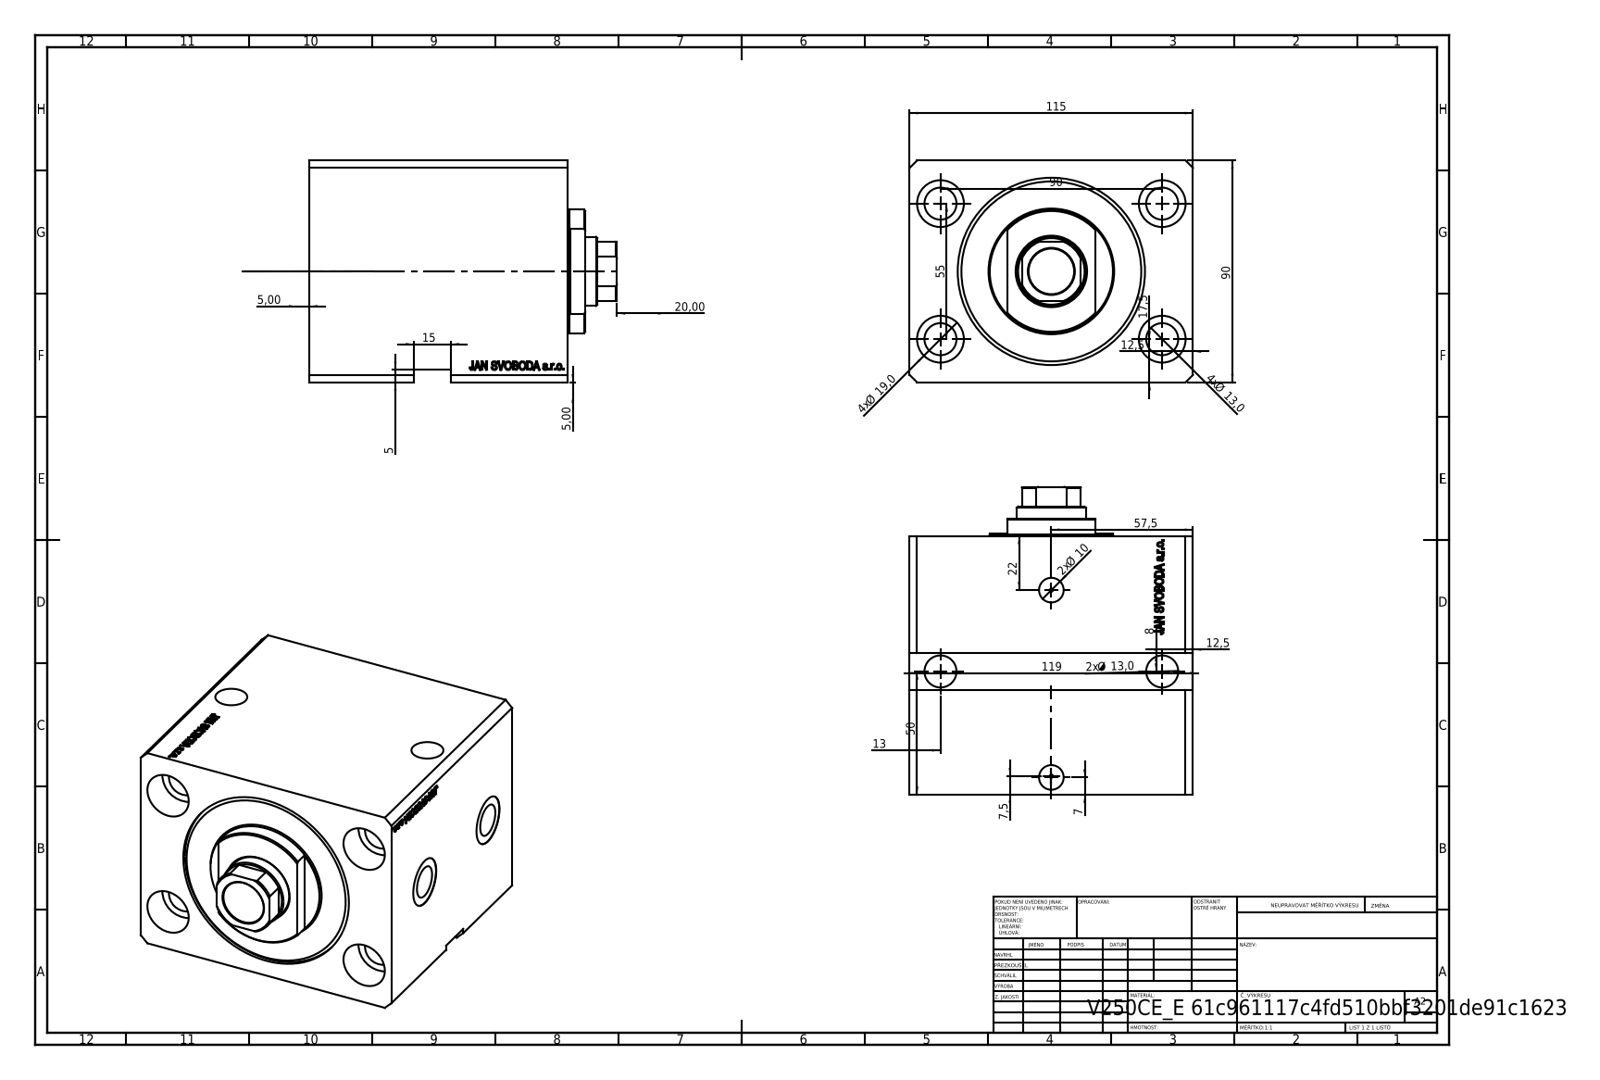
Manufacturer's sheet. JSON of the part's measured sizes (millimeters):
{"part_name": "V250CE_VC_E; V250CE_C_VCP; V250CE_E_Body", "step_written_by": "SolidWorks 2019 (CONFIG_CONTROL_DESIGN)", "units": "millimeters", "bodies": {"solids": 3, "faces": 937, "planar": 467, "cylindrical": 84, "other": 386}, "overall_size": [124.9, 115, 90], "volume_mm3": 942929, "surface_area_mm2": 146742, "round_holes": [[13, 6], [1.25, 4], [19, 4], [10, 2], [13.16, 2], [20, 2], [18.5, 1], [28, 1], [63, 1], [76, 1]], "round_bosses_or_shafts": [[50, 1]], "partial_cylinders_radius": [[13.5, 1]], "face_to_face_distances": [90, 115, 105, 87.1, 17.9, 57, 74.9, 30.1, 20, 54.9], "hole_center_spacings": [52.74, 55, 90, 55.8, 61.88, 62.24, 105.48, 0.53]}
